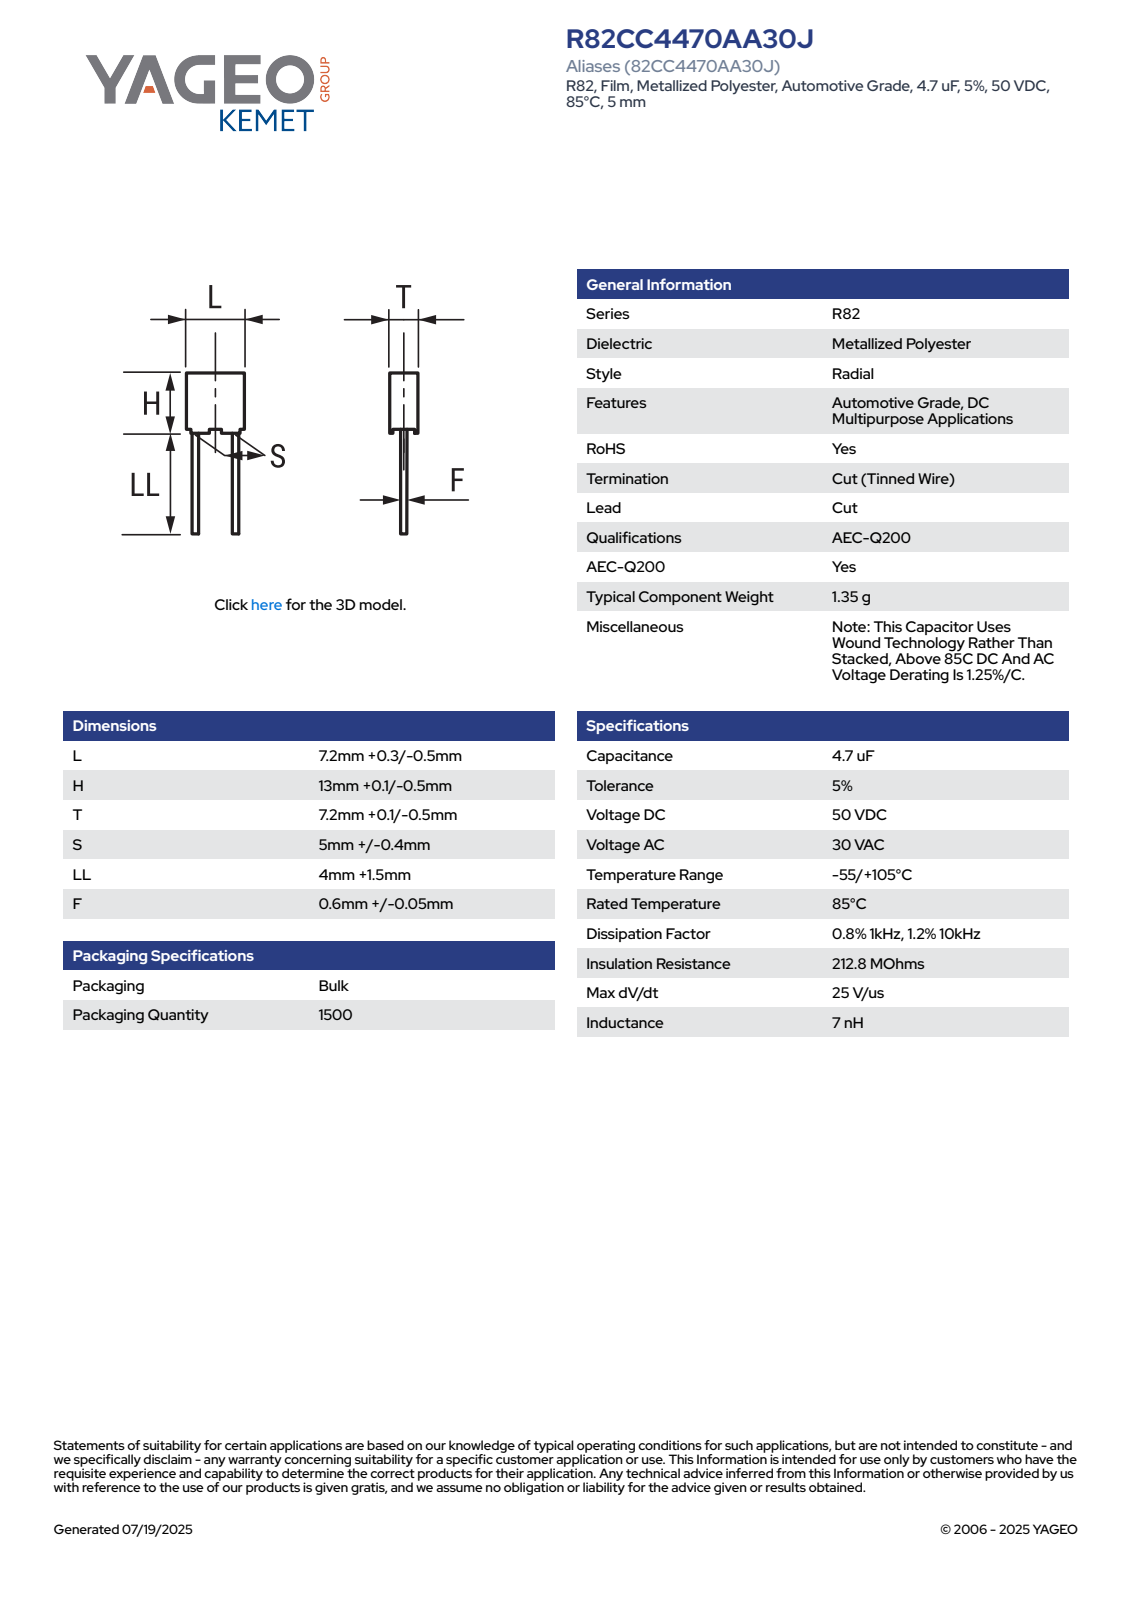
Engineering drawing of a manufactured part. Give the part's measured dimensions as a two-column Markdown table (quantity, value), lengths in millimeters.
| quantity | value |
| --- | --- |
| part name | CFR_RB3_7.2X13X7.2_L7.5H13.1T7.3S5LL5.5F0.65 |
| STEP written by | SolidWorks 2014 (AUTOMOTIVE_DESIGN) |
| units | millimeters |
| bodies | 4 solids, 85 faces (77 planar, 8 cylindrical, 0 other) |
| overall size | 18.6 × 7.5 × 7.3 |
| volume | 684 mm³ |
| surface area | 538 mm² |
| round bosses / shafts (diameter × count) | 0.65 × 2 |
| partial cylindrical surfaces (radius × count) | 0.5 × 4 |
| main face-to-face distances | 7.3, 7.5, 12.35, 7.25, 7.05, 0.75, 13.1, 7, 6.8, 0.45 |
